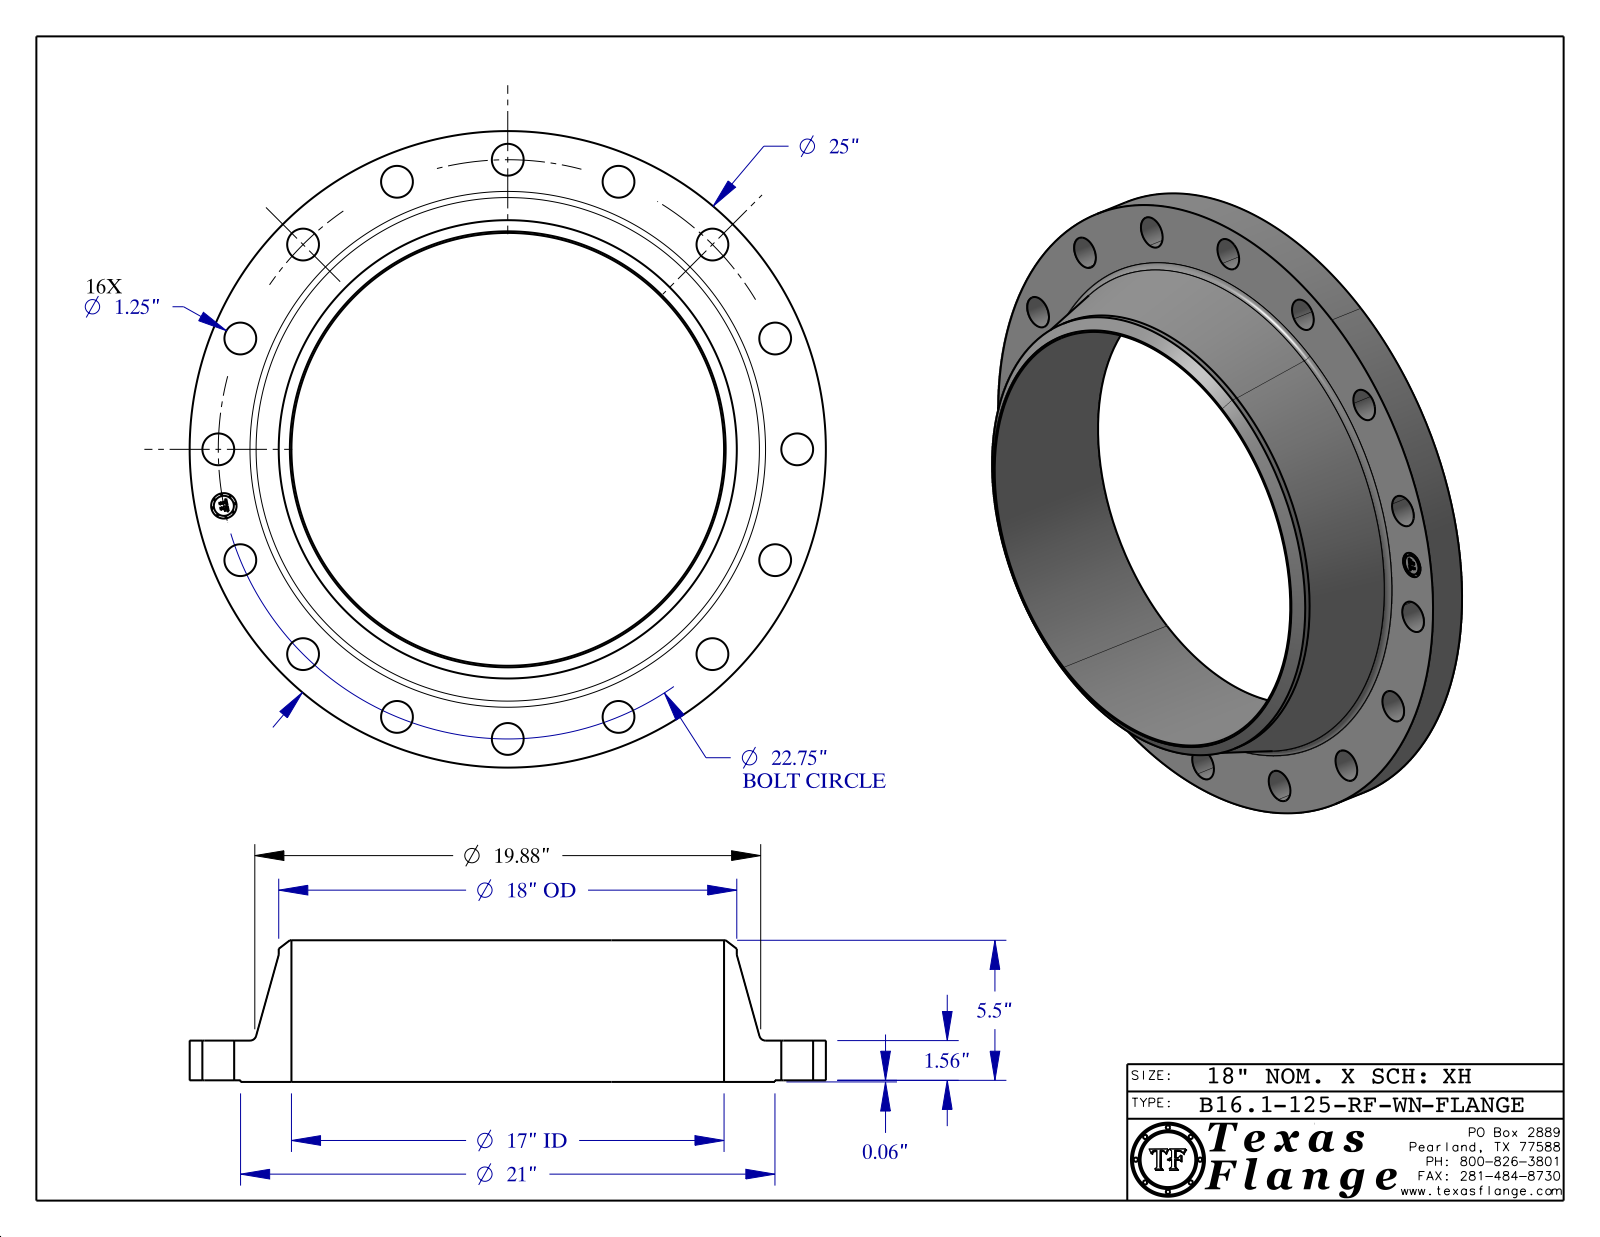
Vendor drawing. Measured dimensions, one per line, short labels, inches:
name: B16.1, Class 125-RF-WN
written by: CATIA V5 STEP AP214 (AUTOMOTIVE_DESIGN)
unit: in
bodies: 1 solid, 435 faces (369 planar, 60 cylindrical, 6 other)
size: 25 × 25 × 5.563
volume: 585.8 in³; area: 1 179 in²
holes: 16× ⌀1.25, 1× ⌀1, 1× ⌀17
bosses: 8× ⌀0.061, 1× ⌀25, 1× ⌀21, 1× ⌀18, 1× ⌀0.788
face distances: 1.56, 0.063, 1.623, 5.563, 5.5, 3.94, 1.608, 1.545, 0.015, 3.955
hole spacings: 12.639, 22.313, 11.375, 8.706, 16.087, 21.019, 4.438, 4.439
